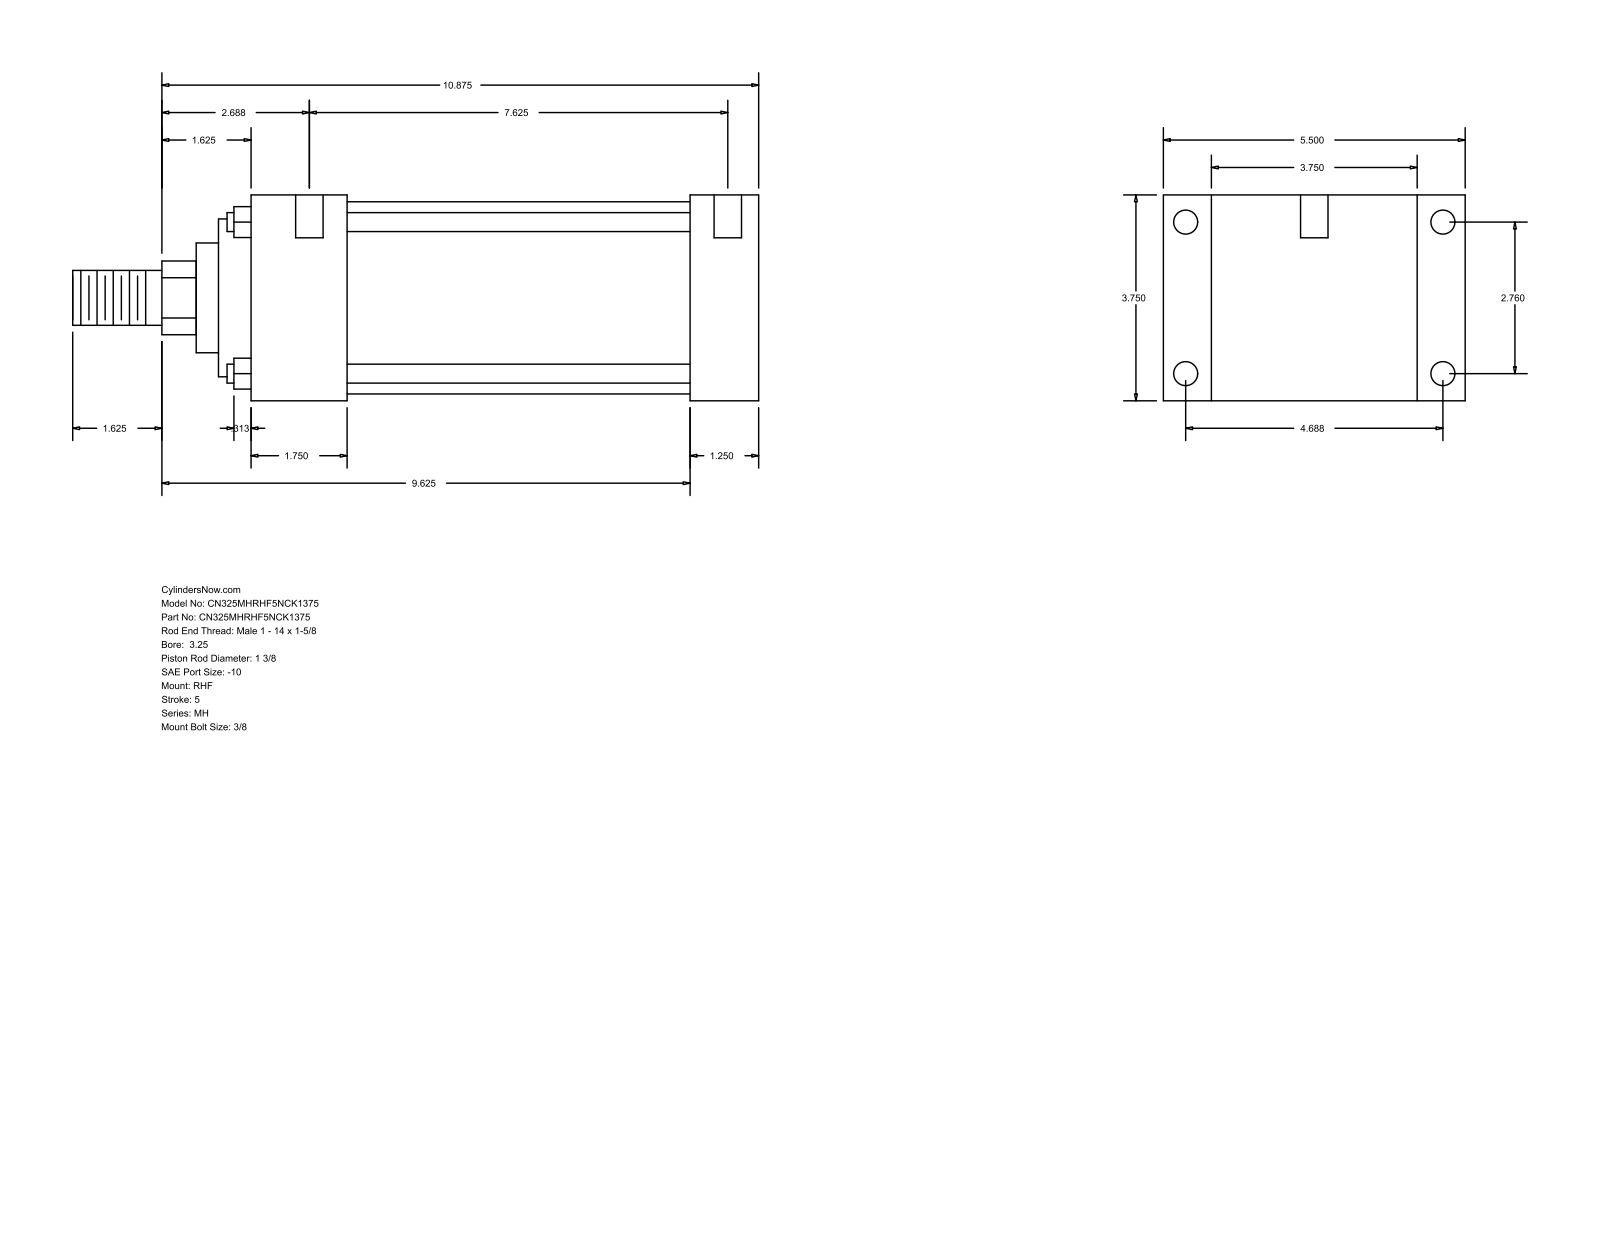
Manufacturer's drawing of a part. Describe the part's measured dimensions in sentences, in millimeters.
The part is named "MH_RHF__0325_1.375". Its 3-D file was written by "GSSL Pune (CONFIG_CONTROL_DESIGN)". It is 0 solids with 90 faces: 61 planar, 29 cylindrical and 0 other. Overall it measures 317.5 by 139.7 by 95.25 millimeters. Round holes: 4 of diameter 5.56, 4 of diameter 11.13, 2 of diameter 12.7. Round bosses or shafts: 4 of diameter 8.76, 1 of diameter 88.9, 1 of diameter 73.03, 1 of diameter 50.8, 1 of diameter 34.92, 1 of diameter 25.4. Partial cylindrical surfaces (rounded edges, fillets, slot ends): 1 of radius 17.06. The main face-to-face distances are 95.24, 31.76, 22.23, 117.47, 203.2, 234.96, 139.7, 44.45, 158.75, 190.51. The hole center spacings are 70.1, 119.06, 138.16, 200.03, 1.59, 4.76, 193.68, 195.27.
